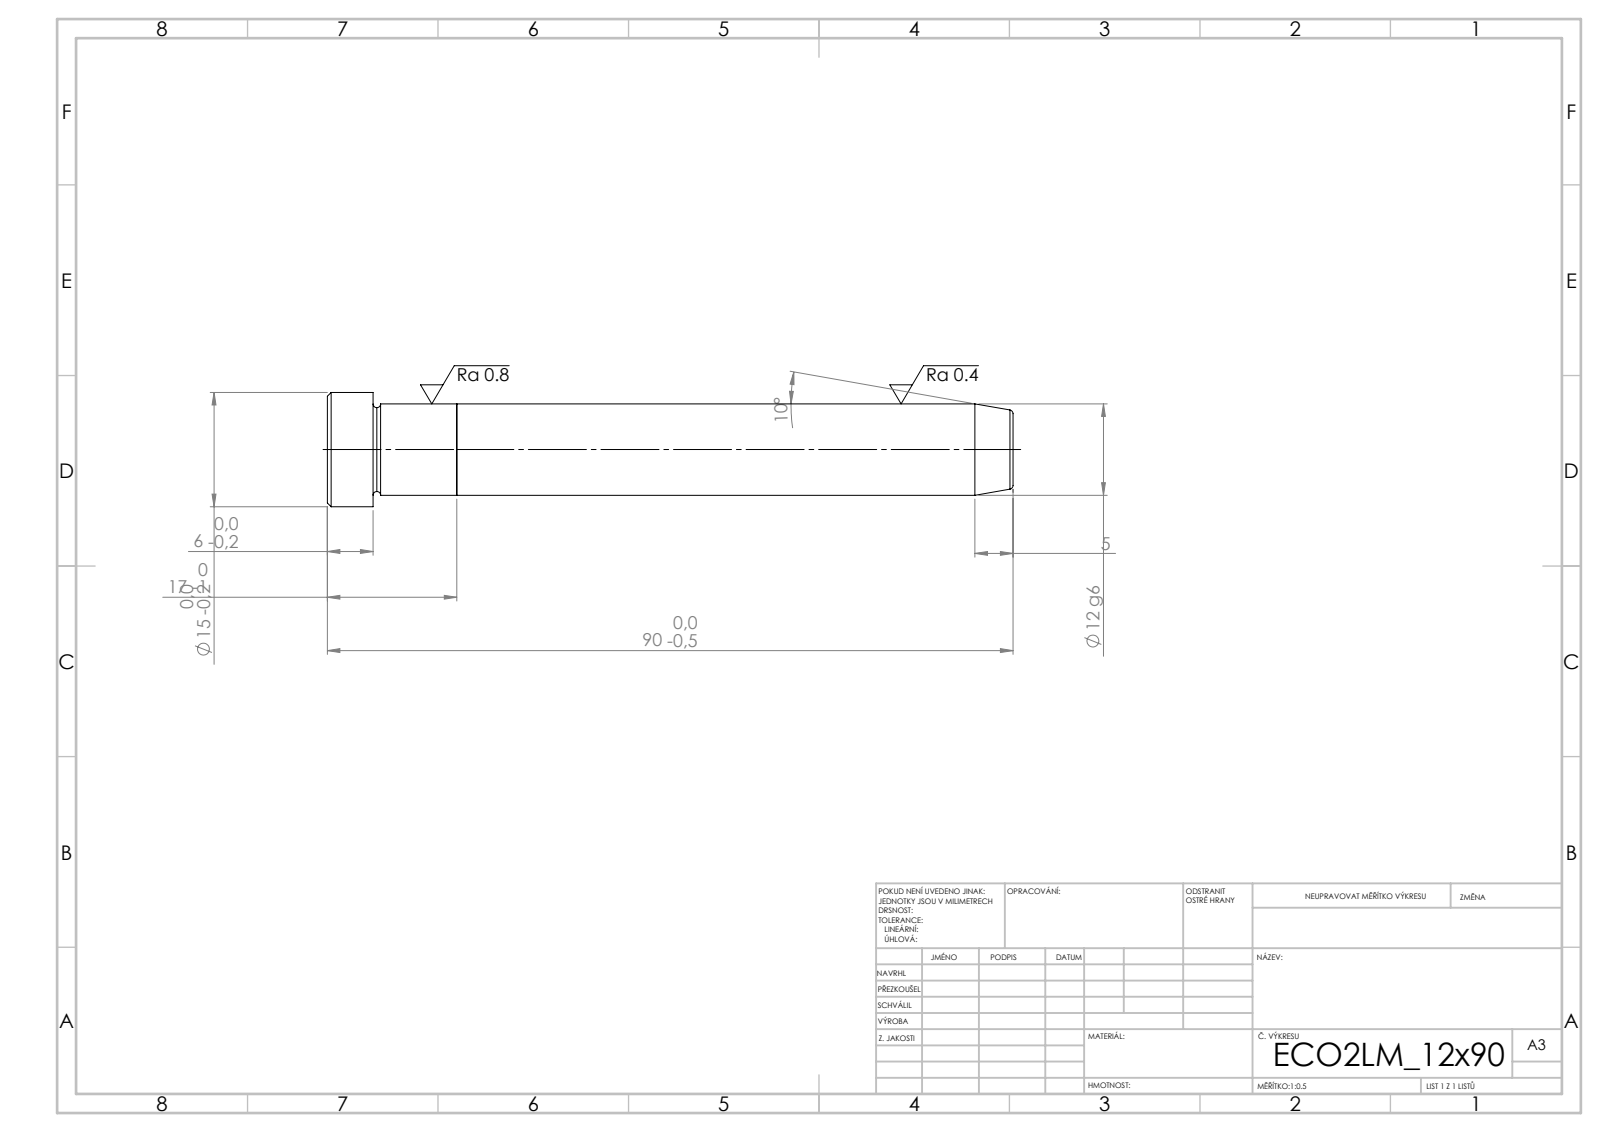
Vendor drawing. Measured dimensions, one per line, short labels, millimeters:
written by: SolidWorks 2019 (CONFIG_CONTROL_DESIGN)
unit: mm
bodies: 2 solids, 21 faces (5 planar, 6 cylindrical, 10 other)
size: 90 × 15 × 15
volume: 10 460 mm³; area: 3 987 mm²
bosses: 1× ⌀15, 1× ⌀12
face distances: 17, 73, 90, 84, 11, 6
